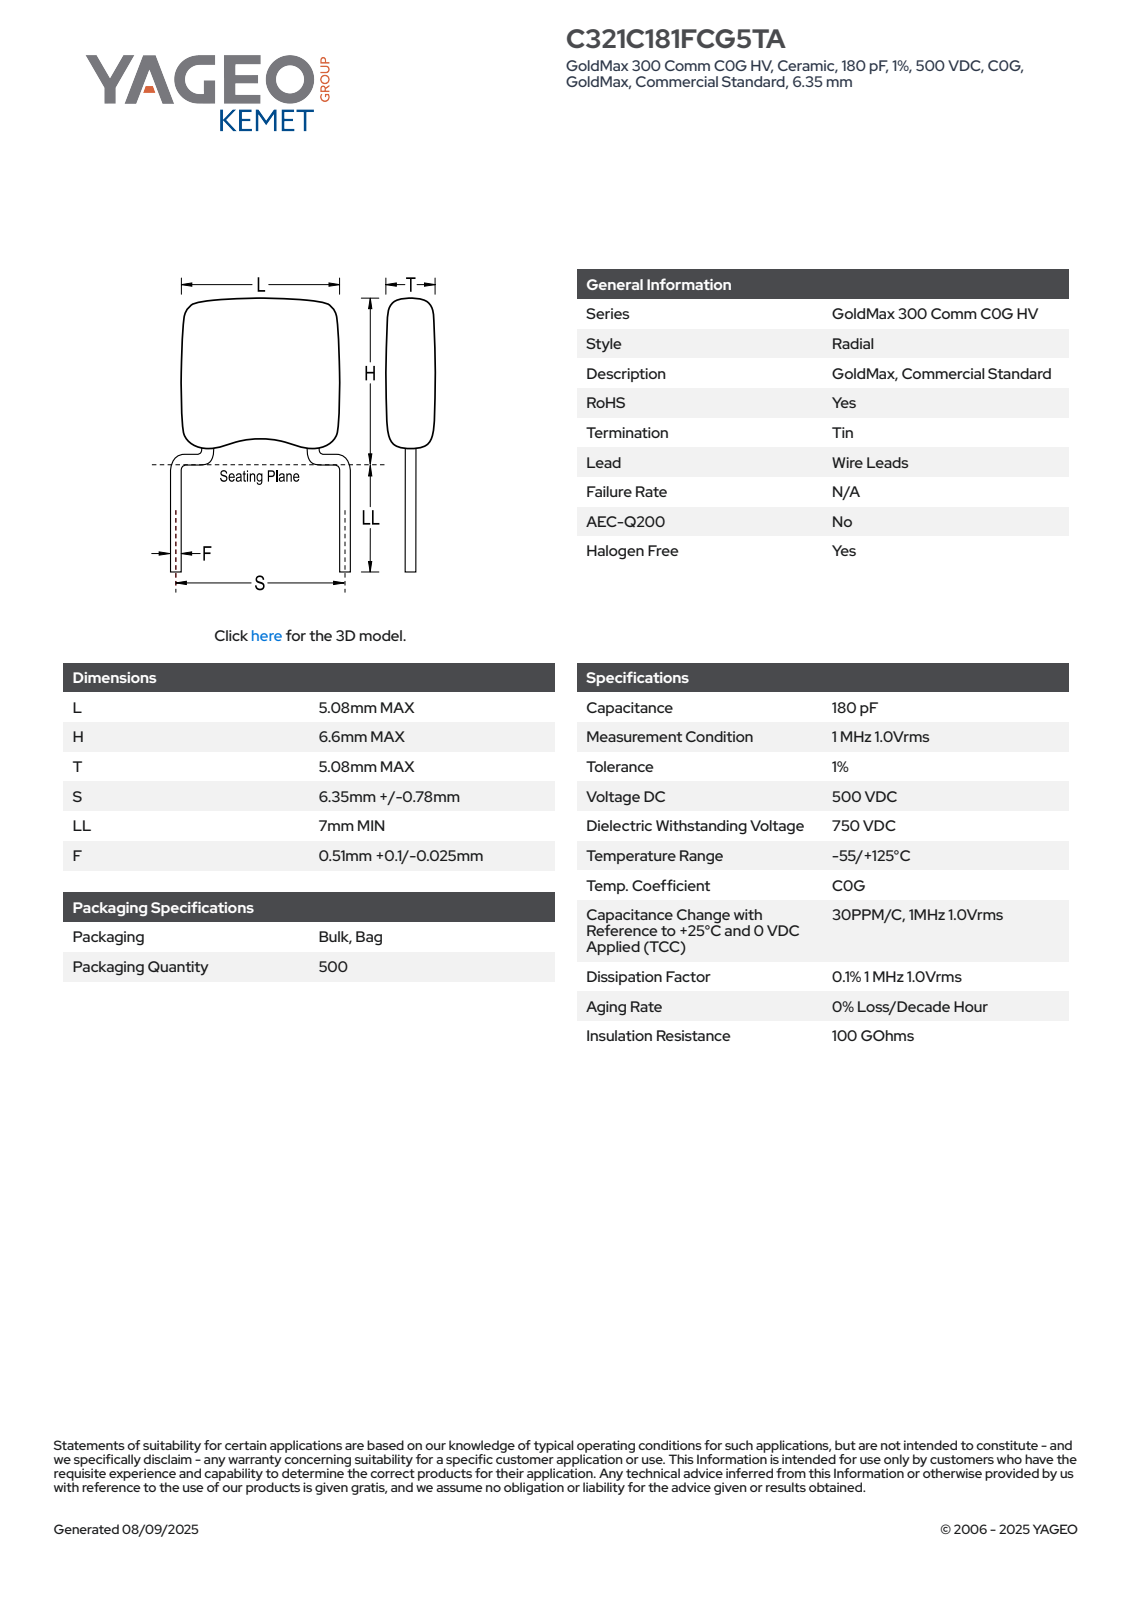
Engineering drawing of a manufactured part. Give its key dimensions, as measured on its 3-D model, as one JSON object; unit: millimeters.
{"part_name": "CCR_SB_5.08X6.6_L5.08H6.6T5.08S6.35LL7F0.51", "step_written_by": "SolidWorks 2014 (AUTOMOTIVE_DESIGN)", "units": "millimeters", "bodies": {"solids": 4, "faces": 97, "planar": 65, "cylindrical": 14, "other": 18}, "overall_size": [13.6, 6.86, 5.08], "volume_mm3": 118, "surface_area_mm2": 158, "round_bosses_or_shafts": [[0.51, 2]], "partial_cylinders_radius": [[1, 10]], "face_to_face_distances": [5.08, 4.81, 0.43, 2.64, 2.17, 2.21, 2.6, 0.39, 0.35, 1.76]}
